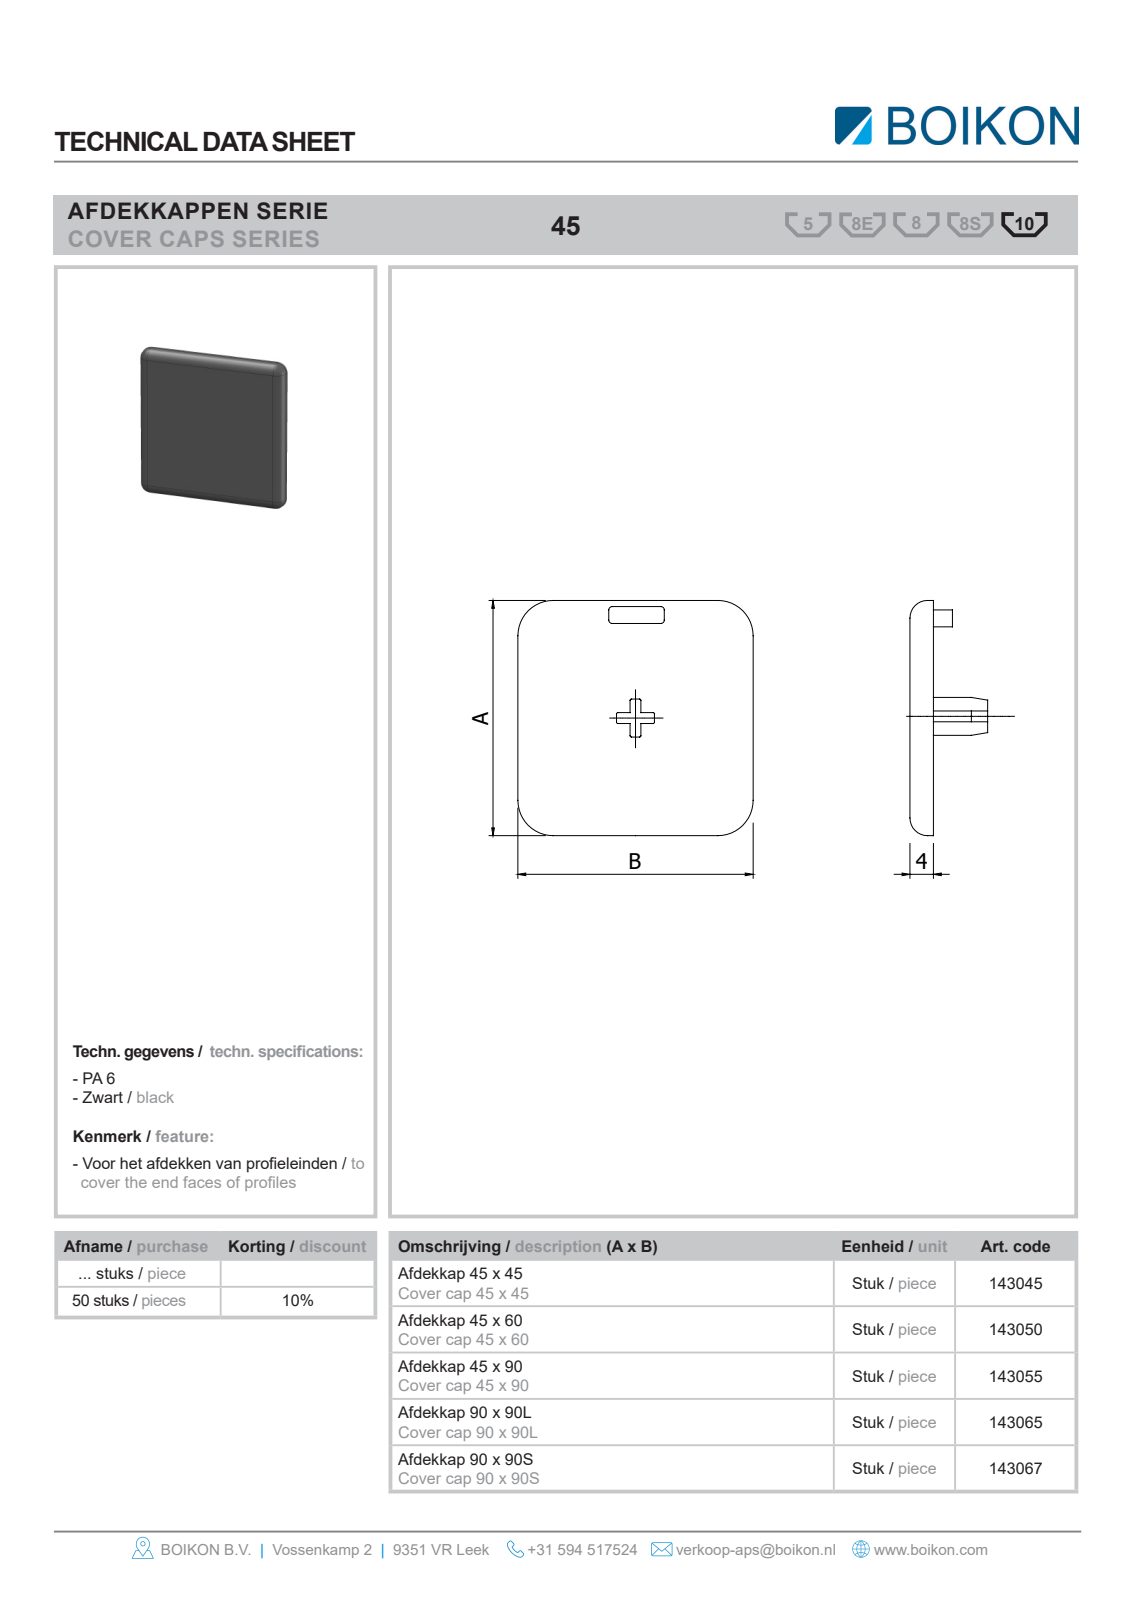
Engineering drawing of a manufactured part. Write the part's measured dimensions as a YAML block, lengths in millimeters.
part_name: "Root; 143045Afdekkap 45 x 45BOIKON"
step_written_by: "HiCAD 2013 1802.4 Build 509 (AUTOMOTIVE_DESIGN)"
units: millimeters
bodies: {solids: 1, faces: 18, planar: 6, cylindrical: 8, other: 4}
overall_size: [45, 45, 4]
volume: 7740
surface_area: 4505
partial_cylinders:
  - {radius: 3, count: 8}
face_to_face_distances: [4, 45]
